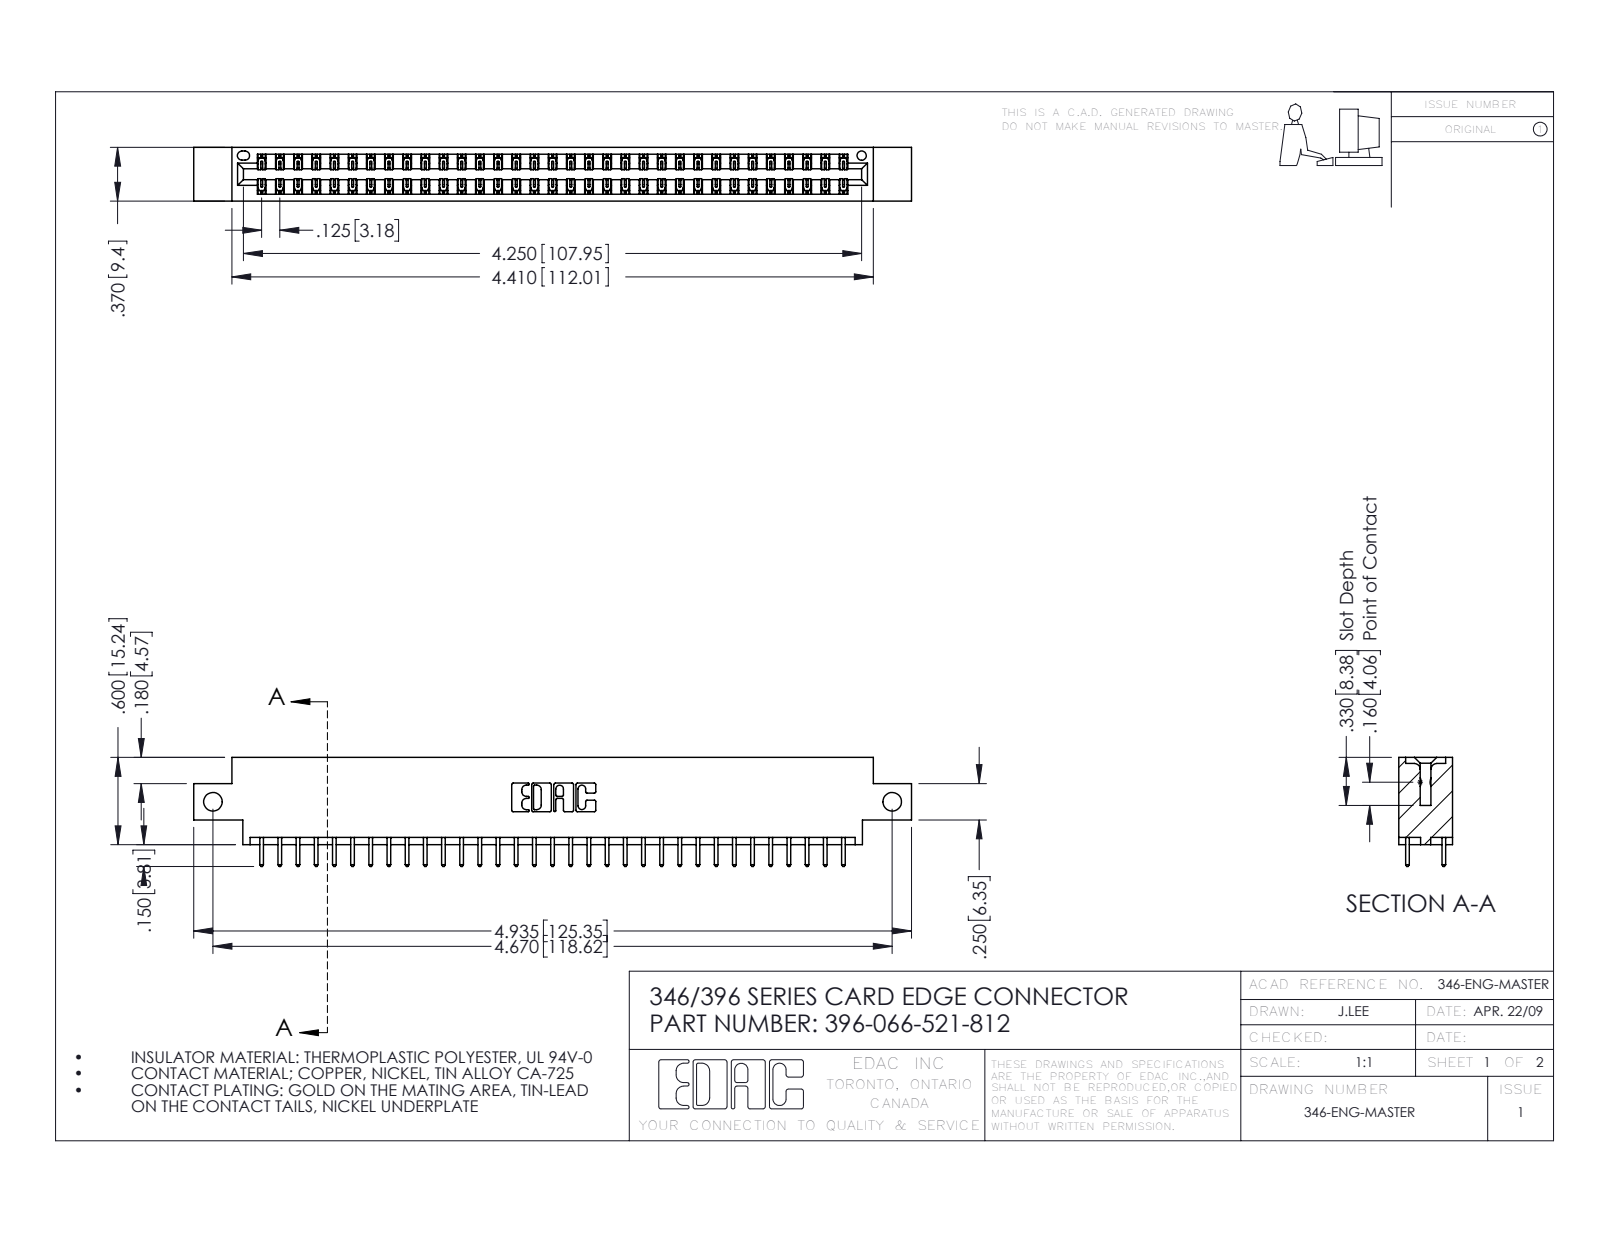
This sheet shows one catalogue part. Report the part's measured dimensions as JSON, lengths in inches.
{"part_name": "396-066-521-812; 346 Part_0.170 Offset - Side Mount; 345-292-001_345-293-121", "step_written_by": "SolidWorks 2016 (CONFIG_CONTROL_DESIGN)", "units": "inches", "bodies": {"solids": 67, "faces": 3558, "planar": 2390, "cylindrical": 1168, "other": 0}, "overall_size": [4.935, 0.75, 0.37], "volume_in3": 0.725, "surface_area_in2": 24.89, "round_holes": [[0.128, 2], [0.064, 1]], "partial_cylinders_radius": [[0.006, 99], [0.01, 66], [0.01, 22], [0.007, 6], [0.031, 6], [0.026, 3], [0.014, 2], [0.022, 2]], "face_to_face_distances": [0.048, 0.322, 0.37, 0.25, 0.072, 0.298, 0.025, 0.275, 0.148, 0.222], "hole_center_spacings": [4.67]}
